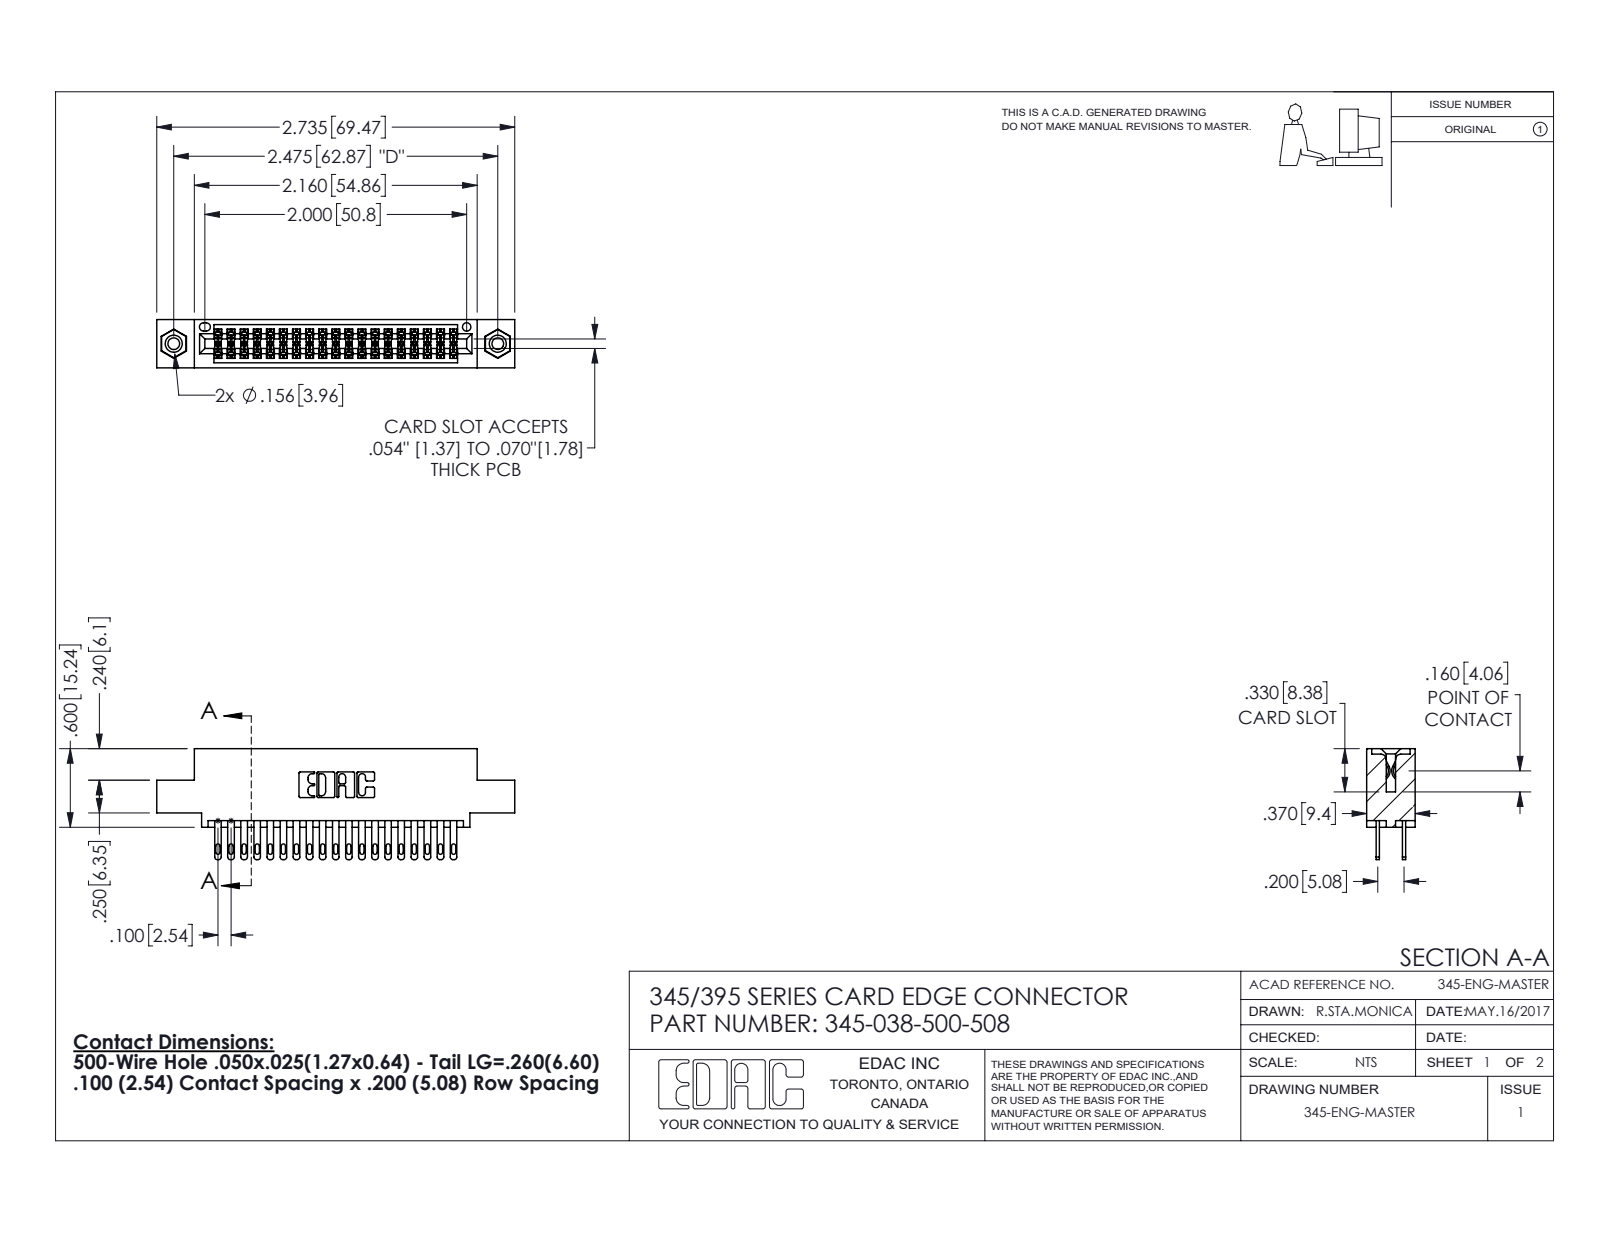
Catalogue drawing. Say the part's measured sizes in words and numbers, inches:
The part is named "345-250-001_345-250-003-102; 345-038-500-508; 345 Part_0.110 Offset - 0.156 Dia-TI; 345-292-001_345-293-100". Its 3-D file was written by "SolidWorks 2016 (CONFIG_CONTROL_DESIGN)". It is 41 solids with 1938 faces: 1142 planar, 780 cylindrical and 16 other. Overall it measures 2.735 by 0.847 by 0.37 inches. Its volume is 0.401 cubic inches and its surface area 15.13 square inches. Round holes: 2 of diameter 0.089, 2 of diameter 0.125, 2 of diameter 0.156, 1 of diameter 0.064. Round bosses or shafts: 2 of diameter 0.155. Partial cylindrical surfaces (rounded edges, fillets, slot ends): 57 of radius 0.006, 38 of radius 0.016, 38 of radius 0.02, 22 of radius 0.01, 6 of radius 0.007, 6 of radius 0.031, 3 of radius 0.026, 2 of radius 0.014. The main face-to-face distances are 0.072, 0.298, 0.2, 0.098, 0.272, 0.025, 0.37, 0.225, 0.175, 0.149. The hole center spacings are 0.27, 2.241, 2.475.
